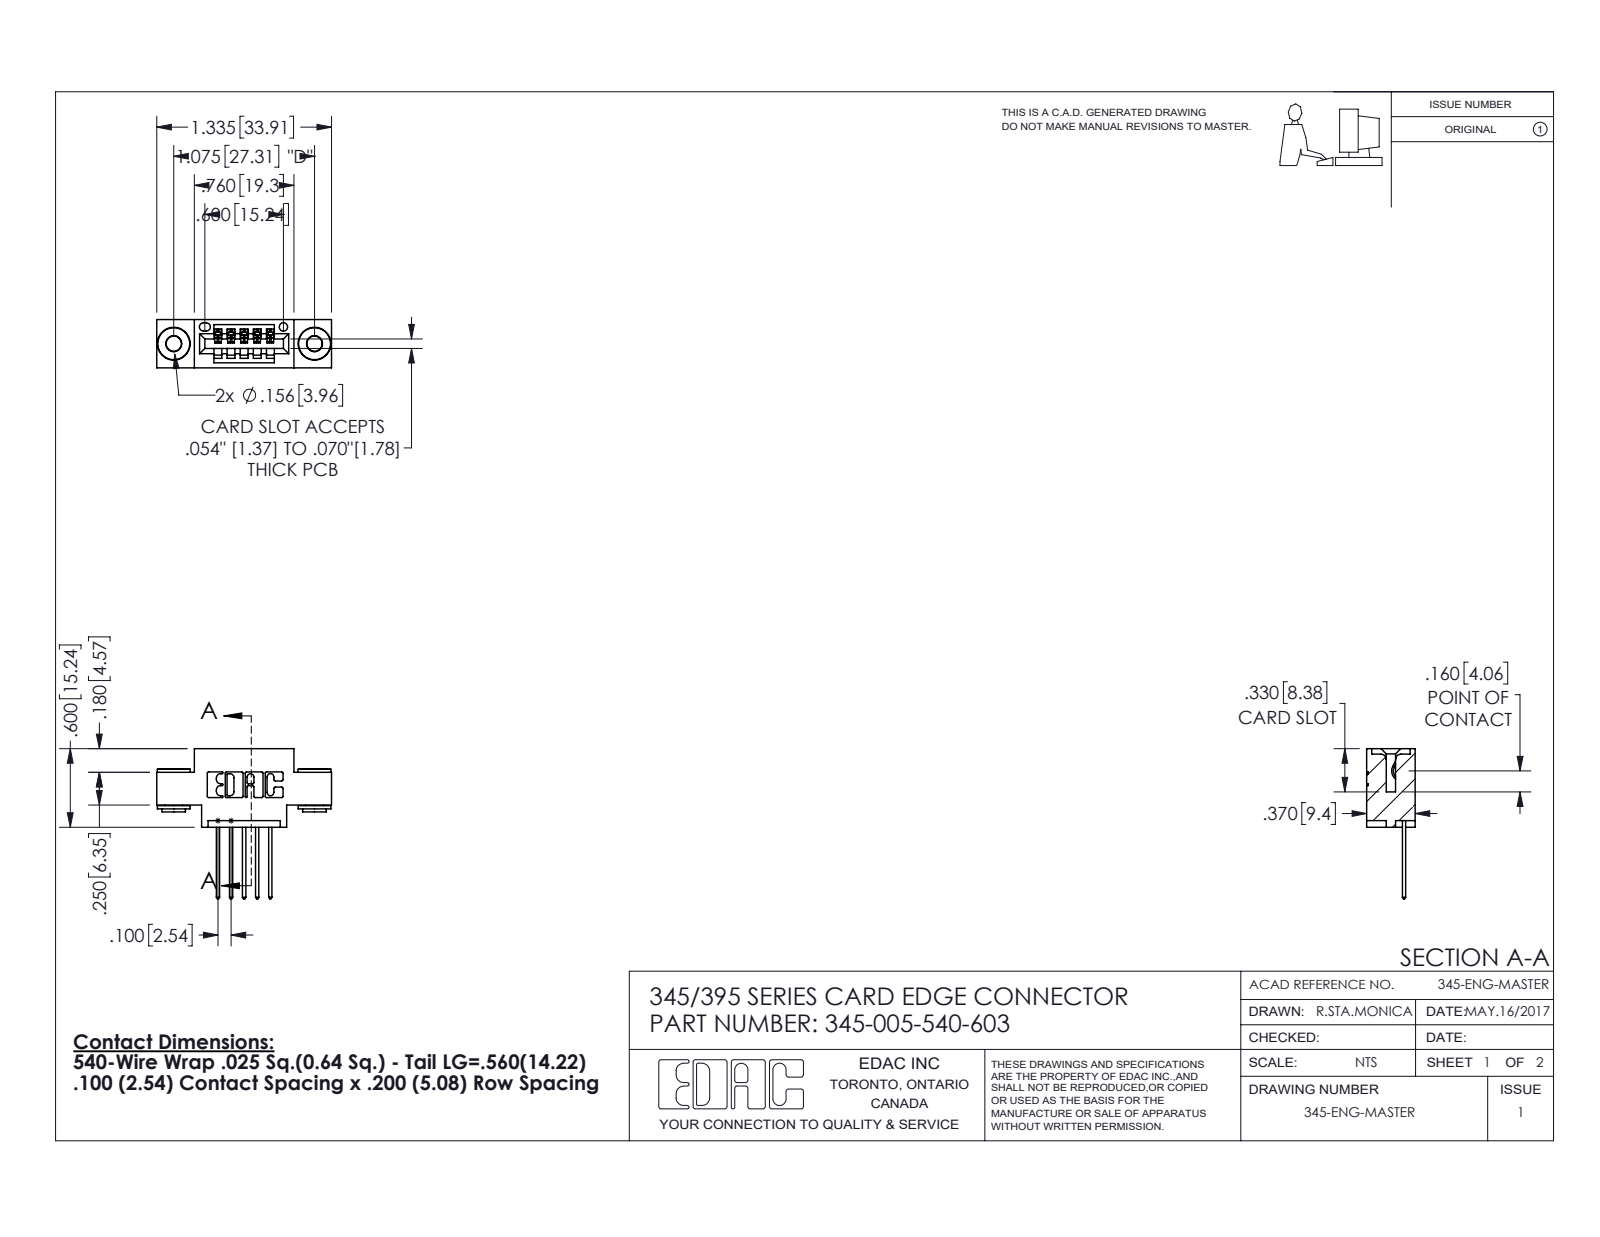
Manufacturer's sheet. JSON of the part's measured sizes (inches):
{"part_name": "345-250-002_345-250-002-102; 345 Part_0.170 Offset - 0.156 Dia-TH; 345-292-001_345-293-140; 345-005-540-603", "step_written_by": "SolidWorks 2016 (CONFIG_CONTROL_DESIGN)", "units": "inches", "bodies": {"solids": 8, "faces": 458, "planar": 294, "cylindrical": 156, "other": 8}, "overall_size": [1.335, 1.147, 0.37], "volume_in3": 0.173, "surface_area_in2": 5.655, "round_holes": [[0.116, 2], [0.156, 2], [0.064, 1]], "round_bosses_or_shafts": [[0.25, 2], [0.18, 2], [0.136, 2]], "partial_cylinders_radius": [[0.01, 22], [0.006, 10], [0.01, 10], [0.007, 6], [0.031, 6], [0.026, 3], [0.031, 2], [0.04, 2]], "face_to_face_distances": [0.37, 0.2, 0.1, 0.072, 0.298, 0.025, 0.25, 0.098, 0.272, 0.06], "hole_center_spacings": [0.27, 0.847, 1.075]}
